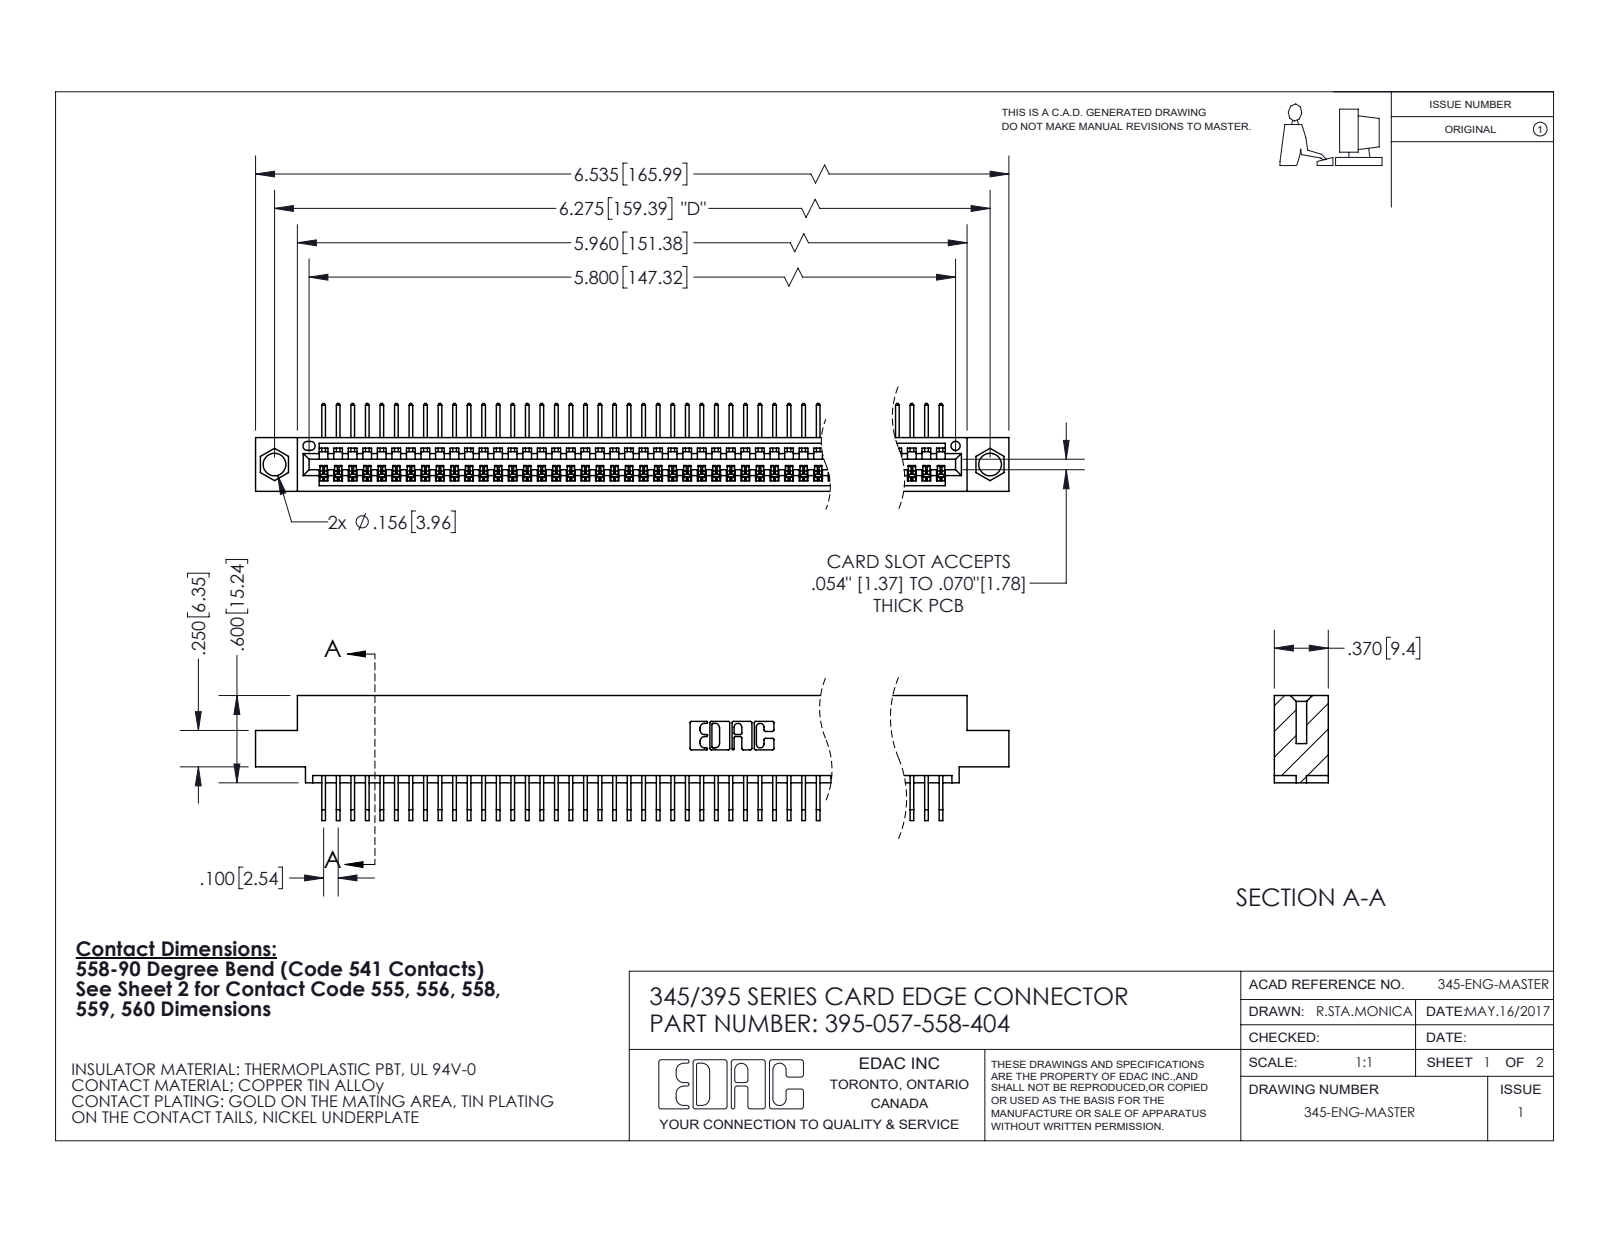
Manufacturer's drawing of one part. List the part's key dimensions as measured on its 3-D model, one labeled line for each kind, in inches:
Part name (STEP PRODUCT): 395-057-558-404; 345 Part_0.110 Offset - 0.156 Dia-TI; 345-292-001_558 Tail - 2
STEP written by: SolidWorks 2020 (CONFIG_CONTROL_DESIGN)
Units: inches
Bodies: 58 solids, 3564 faces (2492 planar, 1072 cylindrical, 0 other)
Overall size (bounding box): 6.535 × 0.859 × 0.605
Volume: 0.97 in³ · Surface area: 34.68 in²
Round holes (diameter × count): ⌀0.156 ×2, ⌀0.064 ×1
Partial cylindrical surfaces — rounded edges, fillets, slot ends (radius × count): R0.006 ×114, R0.01 ×22, R0.007 ×6, R0.031 ×6, R0.026 ×3, R0.031 ×2, R0.04 ×2, R0.014 ×1
Main face-to-face distances: 0.072, 0.298, 0.37, 0.2, 0.098, 0.272, 0.025, 0.225, 0.149, 0.072
Hole centre spacings: 0.27, 6.039, 6.275
